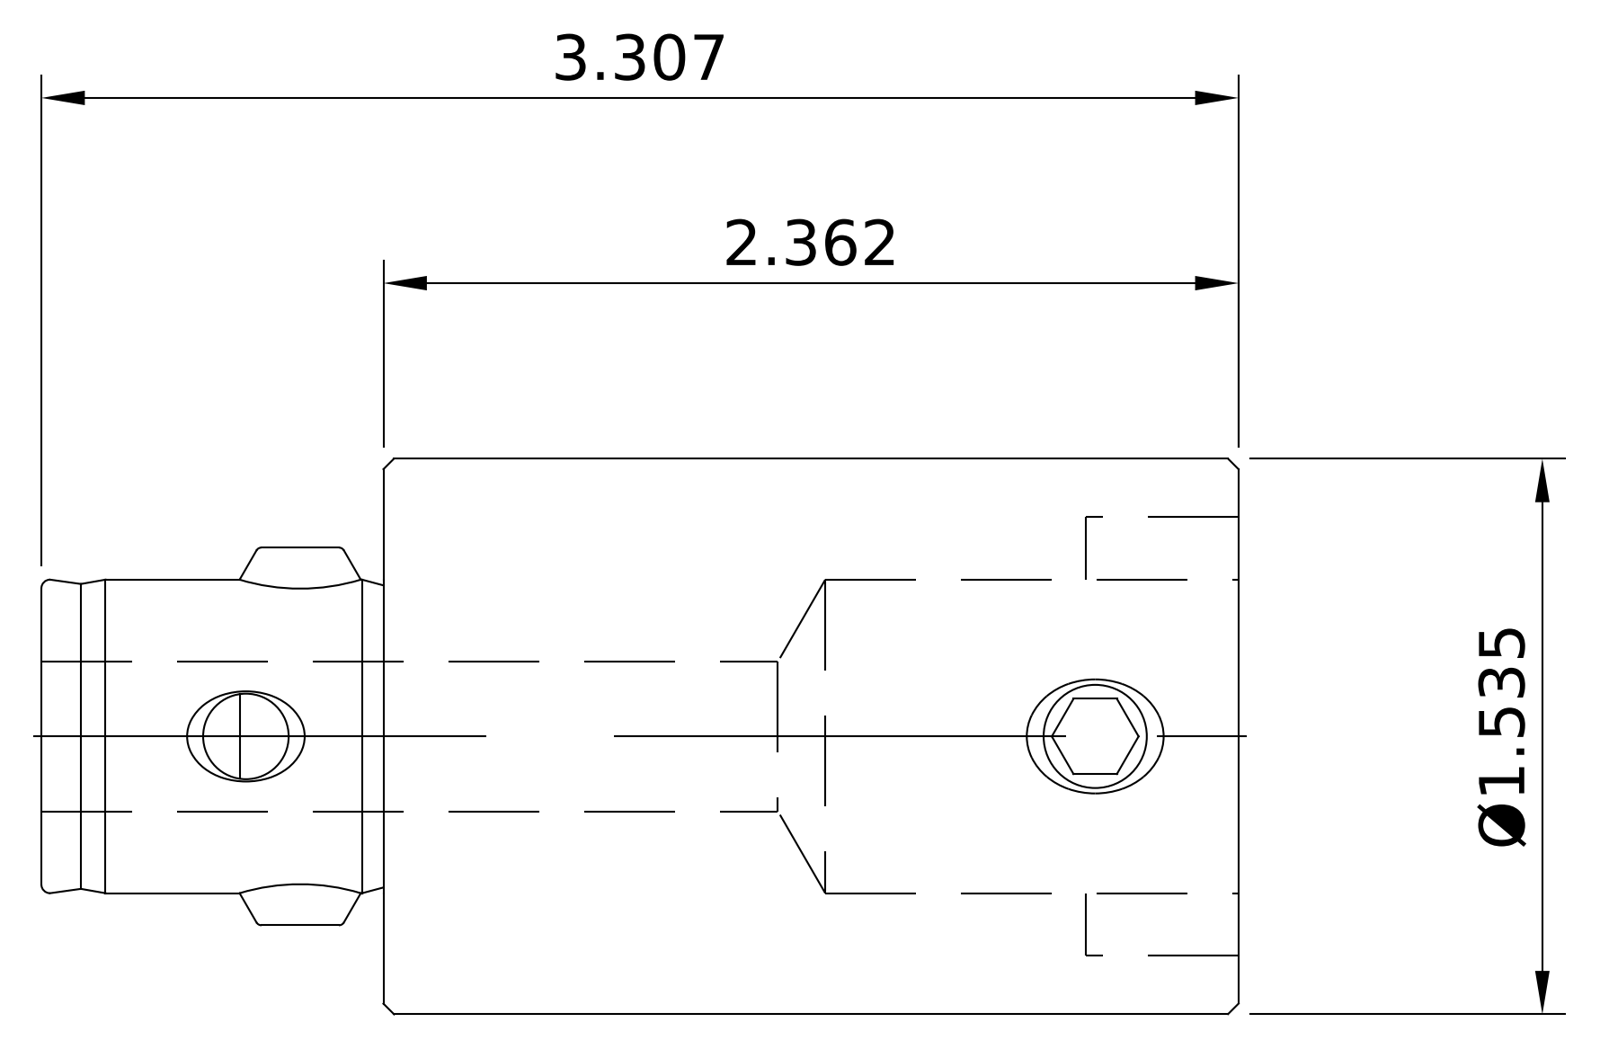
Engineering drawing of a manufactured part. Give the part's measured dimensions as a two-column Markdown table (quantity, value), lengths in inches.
| quantity | value |
| --- | --- |
| part name | 11.331.441; 10.690.43X_10.690.434; 10.691.50X_10.691.504; 691-50XRing_10.691.504Ring |
| STEP written by | SolidWorks 2014 (AUTOMOTIVE_DESIGN) |
| units | inches |
| bodies | 4 solids, 136 faces (39 planar, 45 cylindrical, 52 other) |
| overall size | 3.307 × 1.535 × 1.535 |
| volume | 3.727 in³ |
| surface area | 26.63 in² |
| round holes (diameter × count) | 0.138 × 1, 0.236 × 1, 0.268 × 1, 0.323 × 1, 0.335 × 1, 0.413 × 1, 0.65 × 1, 0.866 × 1, 0.886 × 1 |
| round bosses / shafts (diameter × count) | 1.535 × 1, 1.52 × 1, 0.331 × 1, 0.315 × 1, 0.276 × 1, 0.217 × 1 |
| partial cylindrical surfaces (radius × count) | 0.138 × 2, 0.433 × 1 |
| main face-to-face distances | 2.362, 0.945, 3.307, 2.165, 1.22, 1.142, 0.744, 2.89, 1.945, 0.724 |
| hole center spacings | 0.6, 2.346 |
